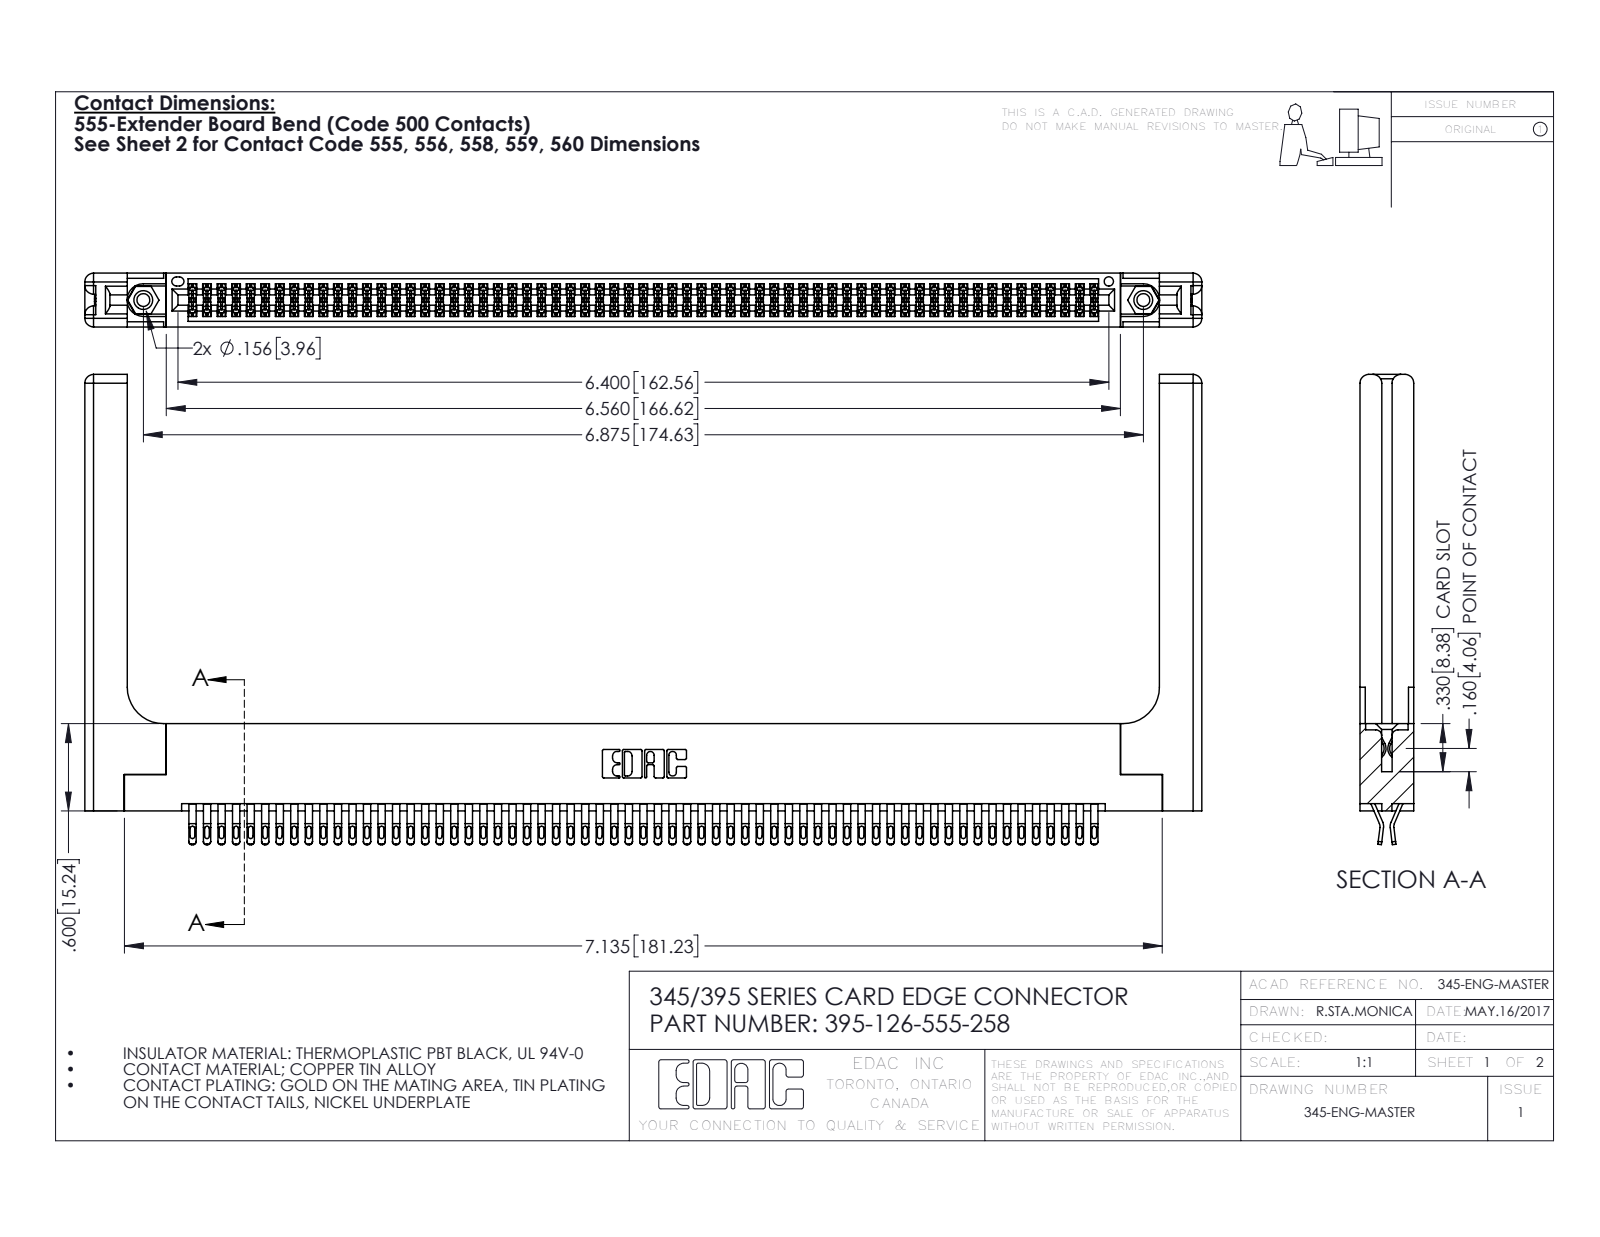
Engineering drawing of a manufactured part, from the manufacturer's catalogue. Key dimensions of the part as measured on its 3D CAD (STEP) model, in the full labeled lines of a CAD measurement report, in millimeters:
Part name (STEP PRODUCT): 345-292-001_555 Tail; 345-220-058_345-220-058; 395-126-555-258; 345-250-001_345-250-001-102 (+1 more)
STEP written by: SolidWorks 2016 (CONFIG_CONTROL_DESIGN)
Units: millimetres
Bodies: 131 solids, 7438 faces (4134 planar, 3244 cylindrical, 60 other)
Overall size (bounding box): 195 × 82.1 × 9.4
Volume: 27 990 mm³ · Surface area: 35 570 mm²
Round holes (diameter × count): ⌀2.3 ×2, ⌀3.2 ×2, ⌀4 ×2, ⌀1.6 ×1
Round bosses / shafts (diameter × count): ⌀3.9 ×2
Partial cylindrical surfaces — rounded edges, fillets, slot ends (radius × count): R0.4 ×315, R0.5 ×252, R0.2 ×189, R0.3 ×22, R1.5 ×16, R0.2 ×6, R0.8 ×6, R0.7 ×3
Main face-to-face distances: 1.8, 7.6, 9.4, 0.6, 5.1, 2.5, 6.9, 5.7, 3.8, 3.8
Hole centre spacings: 6.9, 168.6, 174.6
